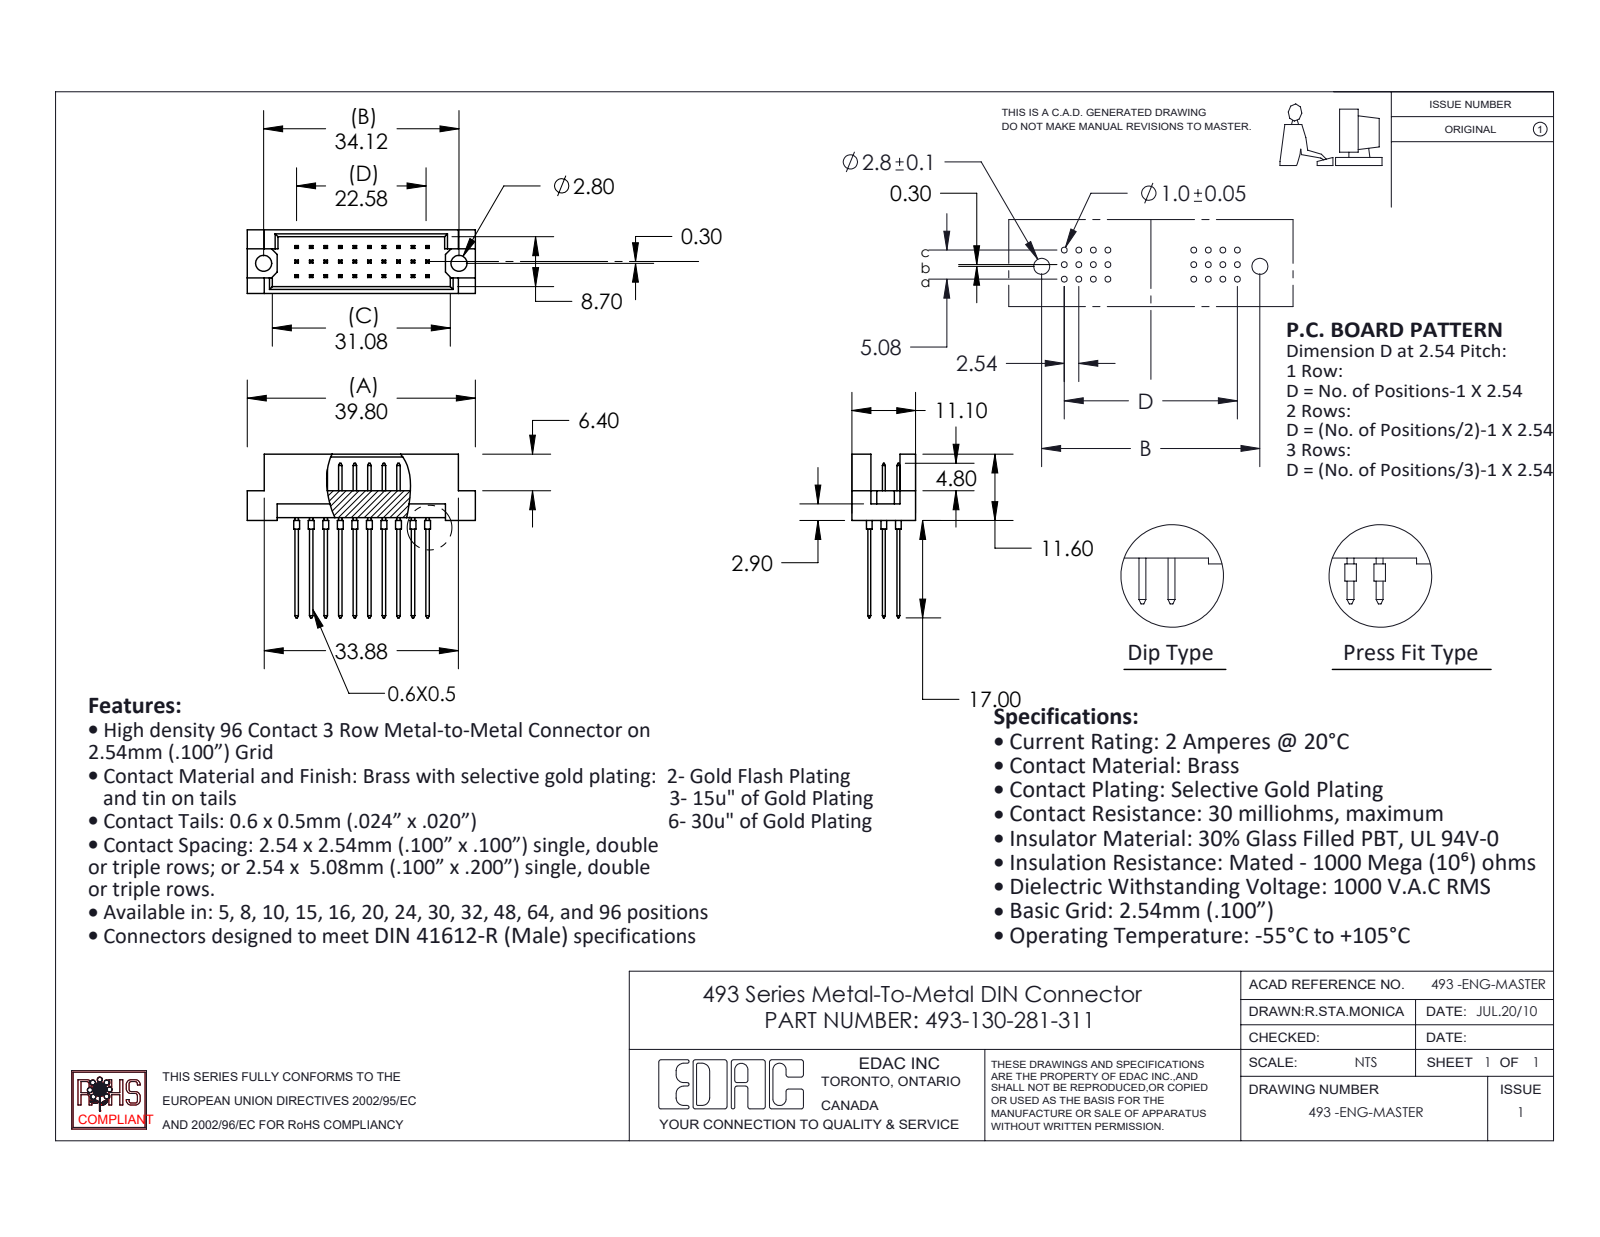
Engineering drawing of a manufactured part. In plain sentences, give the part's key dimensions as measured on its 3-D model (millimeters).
The part is named "493-130-281-311; 493-290_81; 493 Part_30". Its 3-D file was written by "SolidWorks 2020 (CONFIG_CONTROL_DESIGN)". It is 31 solids with 832 faces: 768 planar, 64 cylindrical and 0 other. Overall it measures 39.8 by 28.6 by 11.1 millimeters. Its volume is 2 634 cubic millimeters and its surface area 4 580 square millimeters. Round holes: 2 of diameter 2.8. Round bosses or shafts: 30 of diameter 1. The main face-to-face distances are 2.54, 5.08, 0.5, 7.62, 1.2, 9.9, 10.16, 11.1, 2.76, 3.26. The hole center spacings are 34.12.
